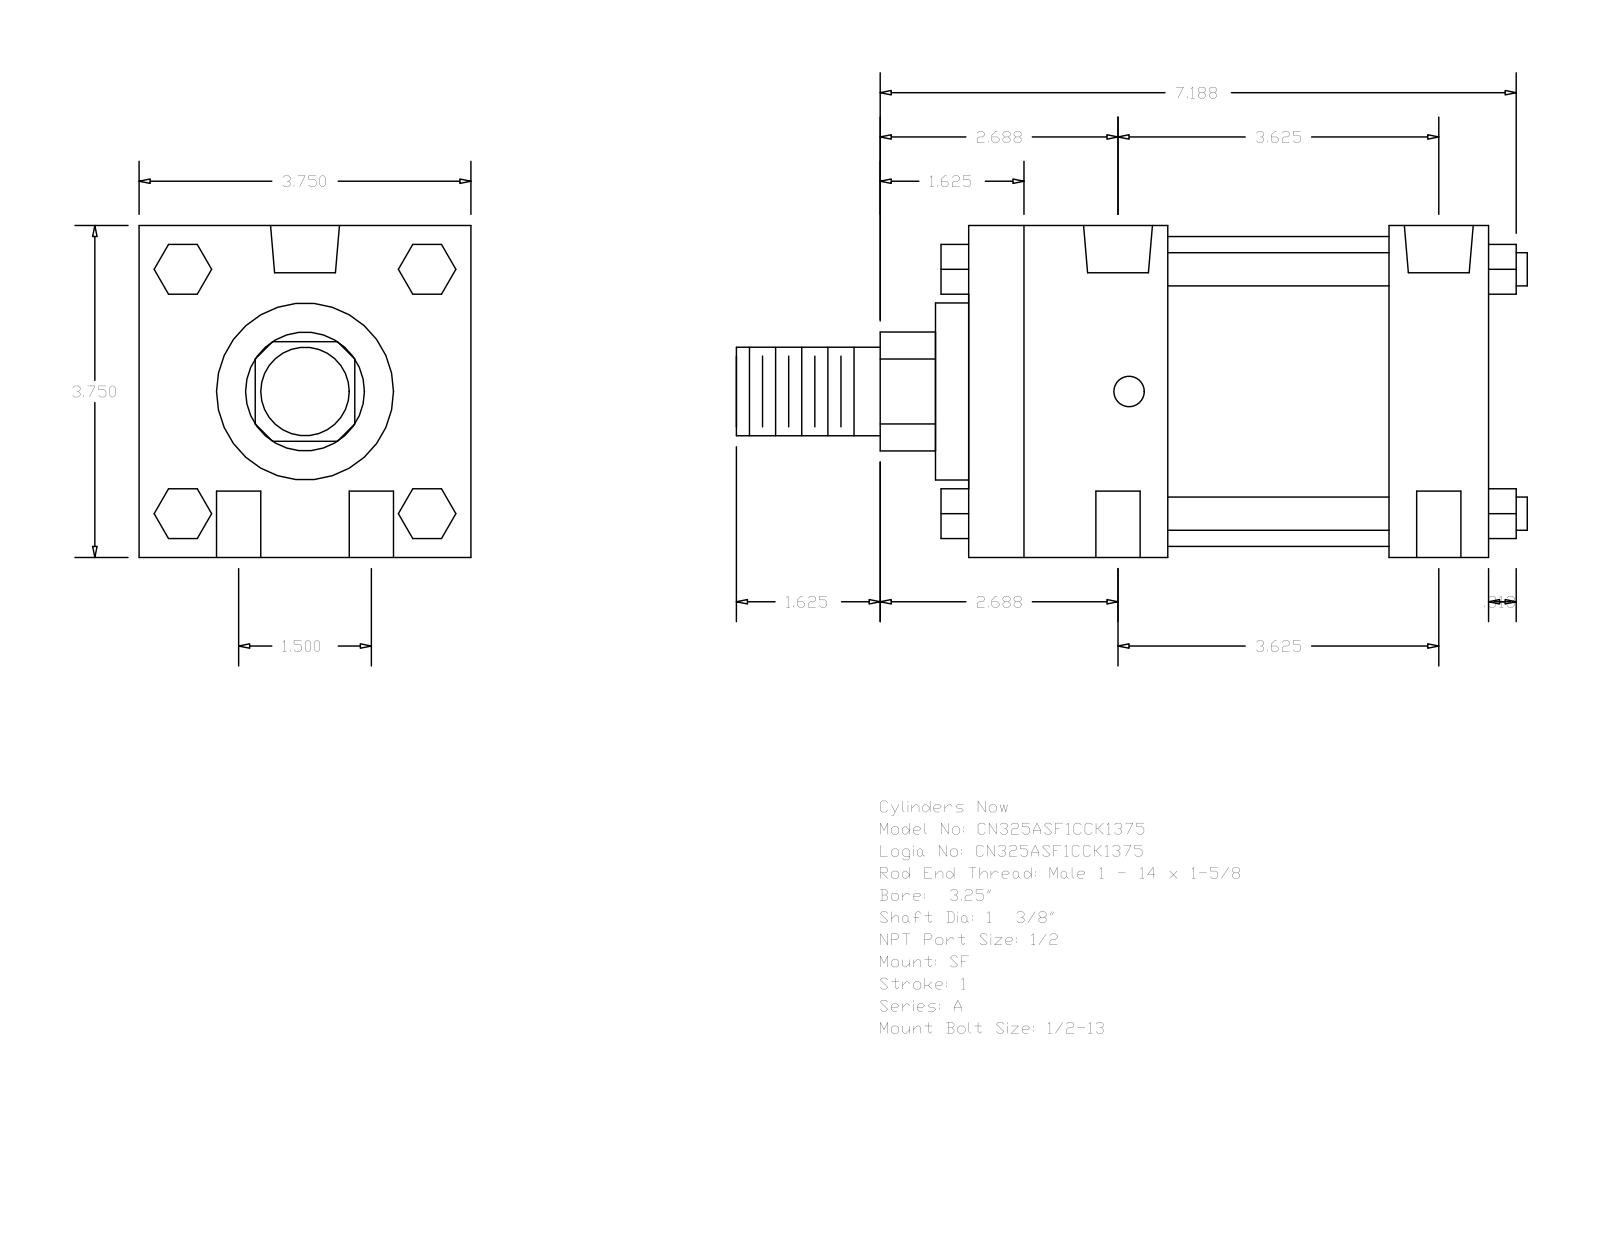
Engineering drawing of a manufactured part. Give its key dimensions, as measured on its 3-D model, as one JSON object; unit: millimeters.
{"part_name": "A_SF__0325_1.375", "step_written_by": "GSSL Pune (CONFIG_CONTROL_DESIGN)", "units": "millimeters", "bodies": {"solids": 0, "faces": 124, "planar": 94, "cylindrical": 30, "other": 0}, "overall_size": [227.01, 95.25, 95.25], "round_holes": [[12.7, 4], [8.73, 2], [19.77, 2]], "round_bosses_or_shafts": [[9.53, 4], [88.9, 1], [50.8, 1], [34.92, 1], [25.4, 1]], "partial_cylinders_radius": [[17.06, 1]], "face_to_face_distances": [95.24, 149.22, 57.15, 120.65, 28.57, 63.5, 92.07, 66.67, 9.52, 130.17], "hole_center_spacings": [19.05, 94.03, 92.08, 38.1, 99.65, 85.72]}
